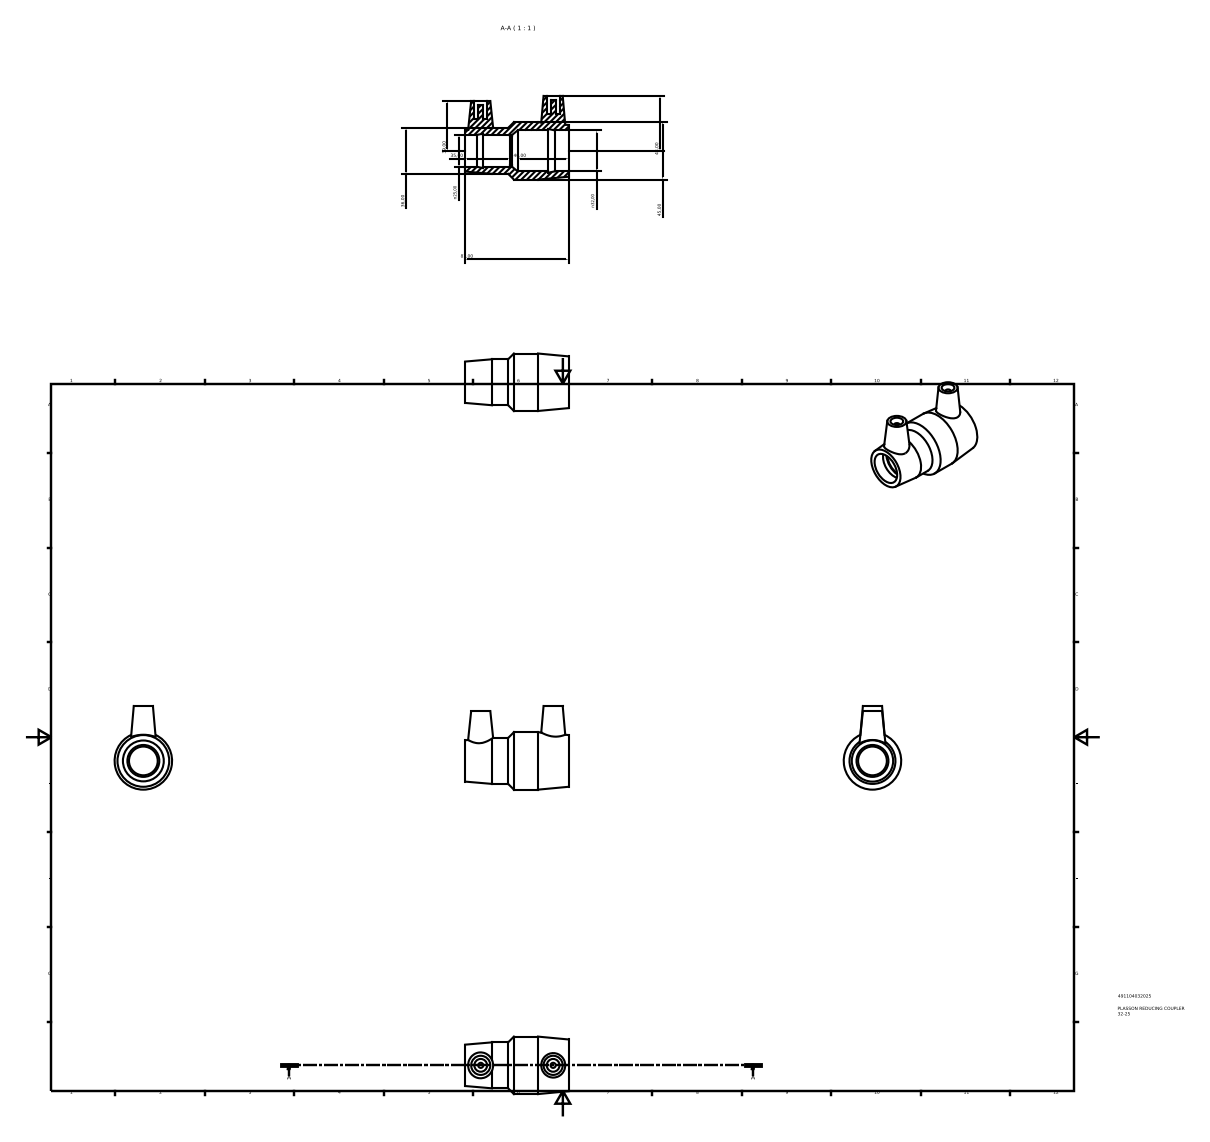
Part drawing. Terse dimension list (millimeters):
name: 491104032025
written by: Autodesk Inventor 2015 (AUTOMOTIVE_DESIGN)
unit: mm
bodies: 1 solid, 32 faces (12 planar, 11 cylindrical, 9 other)
size: 81 × 65.5 × 45
volume: 57 673 mm³; area: 22 456 mm²
holes: 2× ⌀10, 1× ⌀22.5, 1× ⌀25, 1× ⌀32
bosses: 2× ⌀4, 1× ⌀45, 1× ⌀36
face distances: 81, 14, 4, 65, 16, 36.75, 28.25, 44.25, 35, 1.75
hole spacings: 56.7
